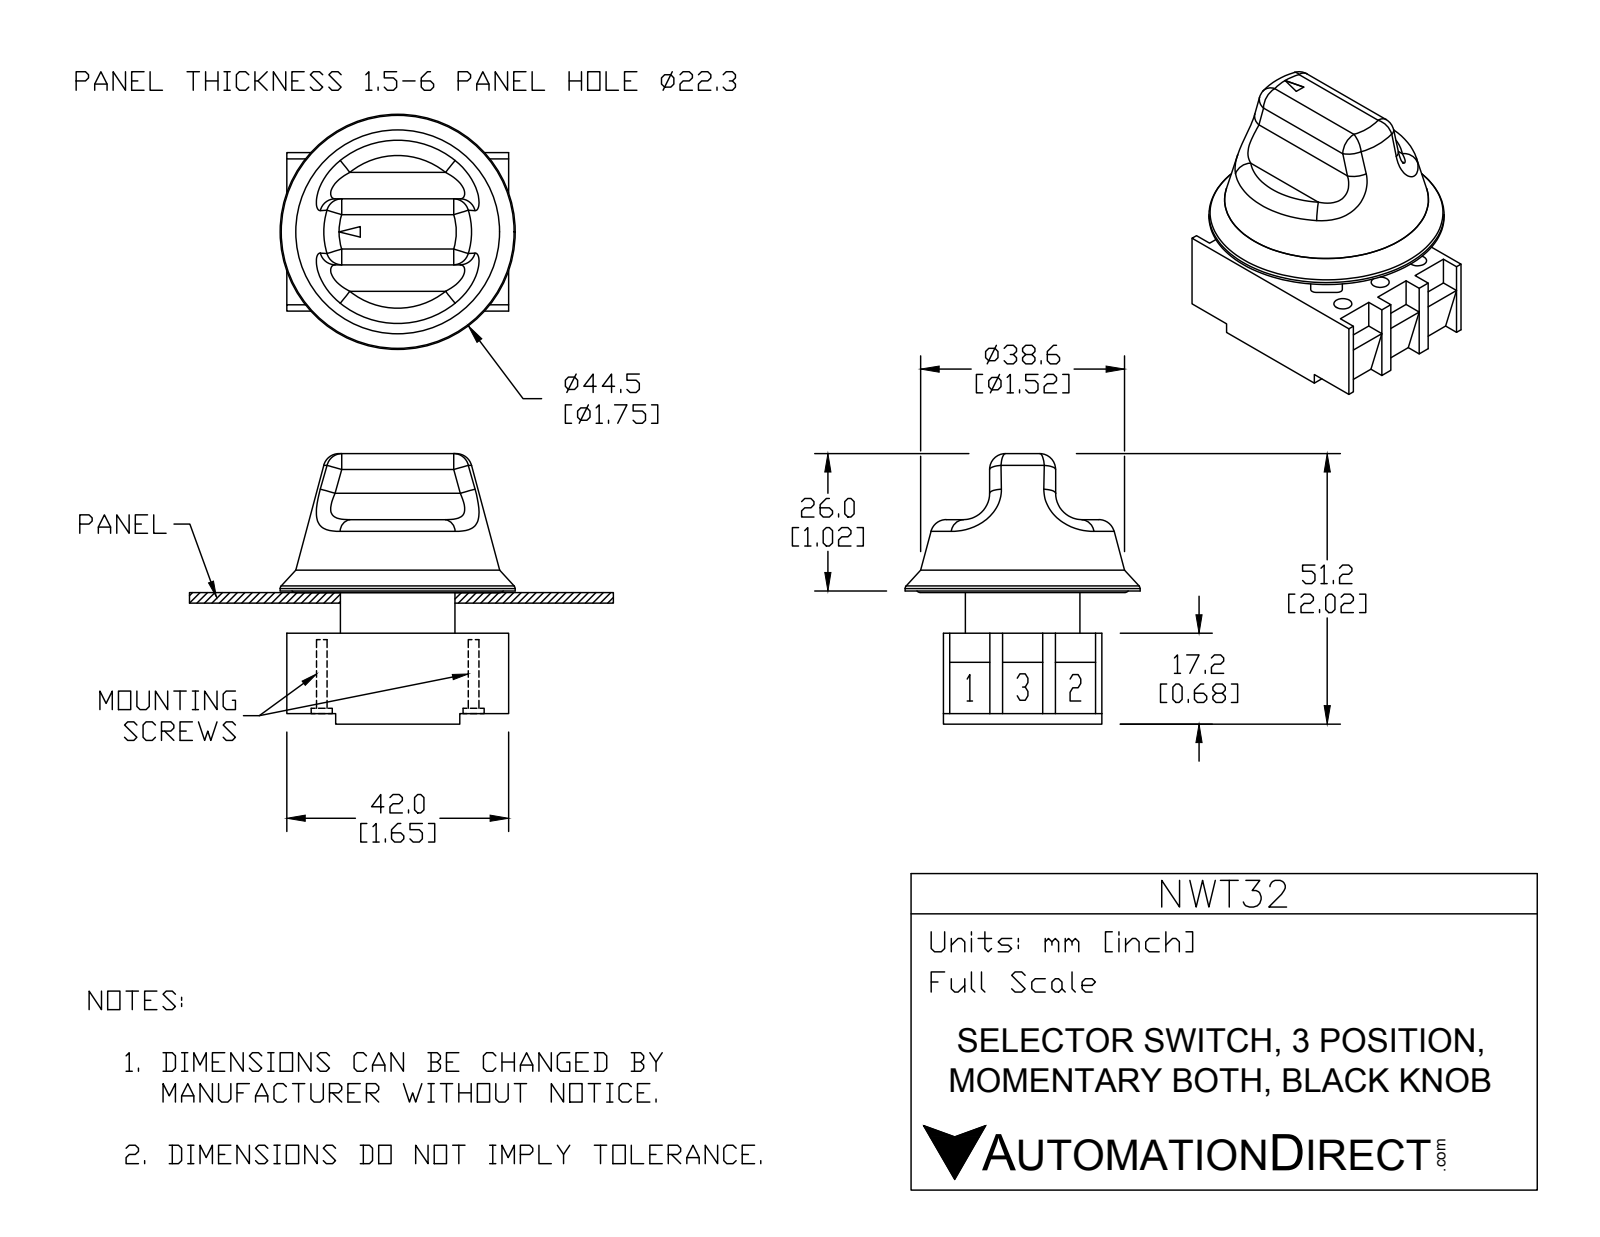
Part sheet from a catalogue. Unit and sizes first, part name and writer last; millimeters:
Units: millimetres
Overall size (bounding box): 51.2 × 44.5 × 44.5
Round holes (diameter × count): ⌀3.4 ×6, ⌀5 ×6, ⌀12.5 ×1
Round bosses / shafts (diameter × count): ⌀4.6 ×2, ⌀4 ×2, ⌀44.5 ×1, ⌀21.7 ×1
Partial cylindrical surfaces — rounded edges, fillets, slot ends (radius × count): R1 ×8, R8.7 ×5, R3 ×2, R5 ×2, R11 ×1
Main face-to-face distances: 3.95, 30, 8, 11.95, 7.7, 4.25, 10, 15.2, 22.9, 23.2
Hole centre spacings: 10, 17.52, 30.45, 28.76, 14.38, 20, 35.03
Volume: 35 027 mm³ · Surface area: 19 099 mm²
Bodies: 7 solids, 236 faces (134 planar, 67 cylindrical, 35 other)
Part name (STEP PRODUCT): NWT32
STEP written by: SolidWorks 2015 (AUTOMOTIVE_DESIGN)
